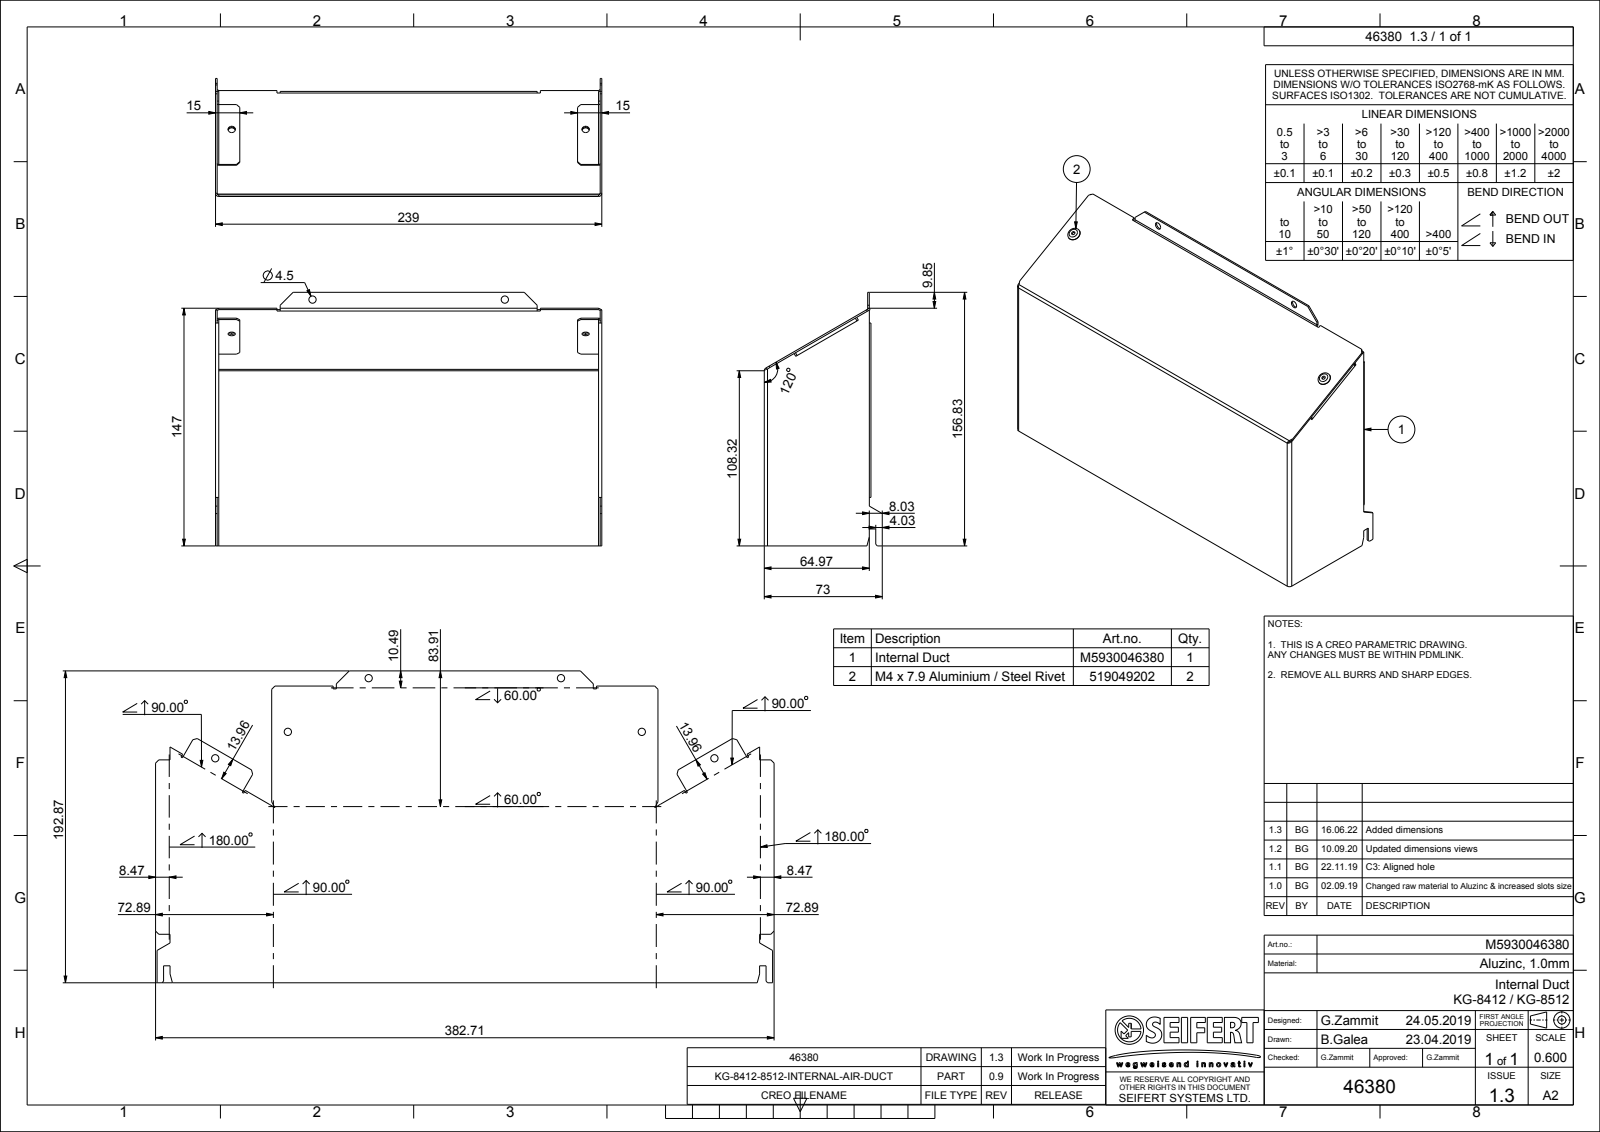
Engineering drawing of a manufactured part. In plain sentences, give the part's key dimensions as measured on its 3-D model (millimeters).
The part is named "KG-8412-8512-INTERNAL-AIR-DUCT". Its 3-D file was written by "CREO PARAMETRIC BY PTC INC, 2023294 (AUTOMOTIVE_DESIGN)". It is 1 solid with 134 faces: 104 planar, 26 cylindrical and 4 other. Overall it measures 219 by 156.83 by 73 millimeters. Its volume is 61 025 cubic millimeters and its surface area 123 471 square millimeters. Round holes: 4 of diameter 4.5. Partial cylindrical surfaces (rounded edges, fillets, slot ends): 8 of radius 1, 6 of radius 2. The main face-to-face distances are 1, 218, 217, 219, 2, 63.98, 216, 64.98, 62.98, 215. The hole center spacings are 119, 199.
